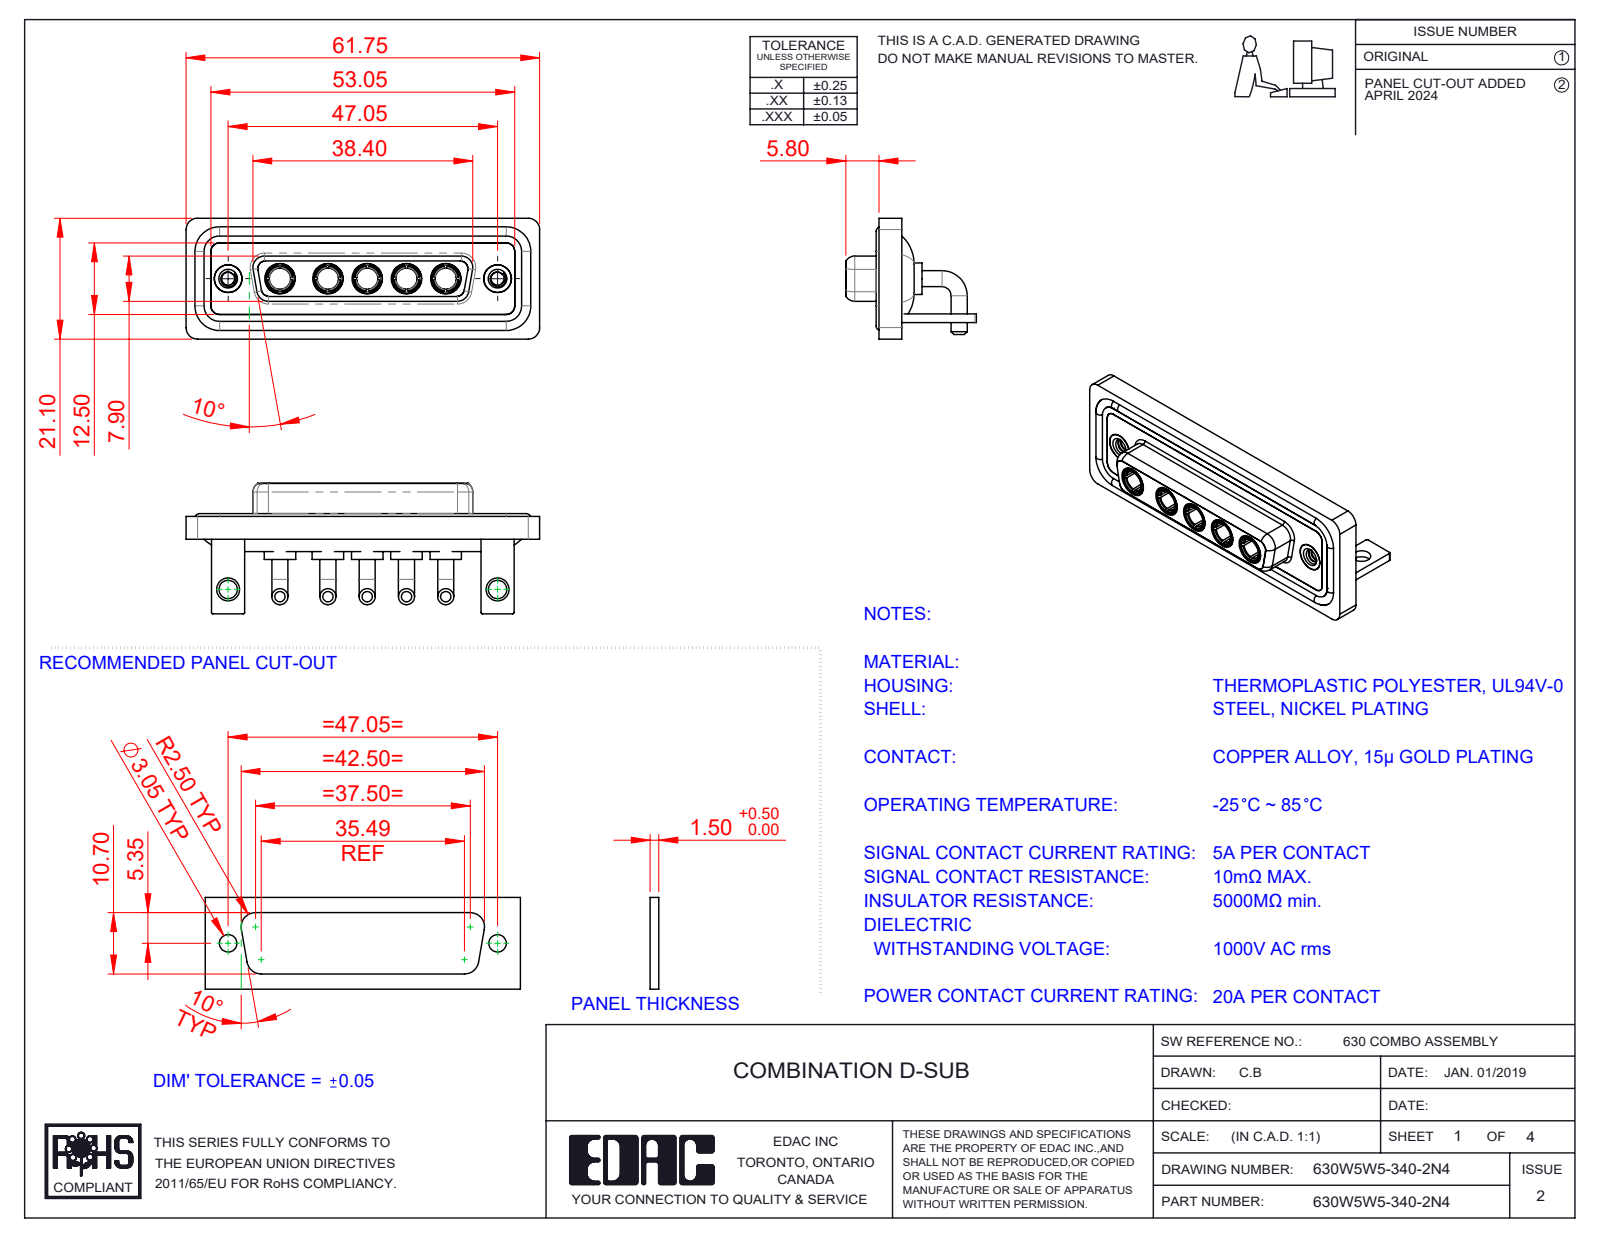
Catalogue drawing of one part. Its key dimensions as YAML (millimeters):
part_name: "630Combo Stabilizer Bracket_50 Contacts; 630Combo Shell Front_25 Contacts; Power Socket_20A RA; 630Combo Housing_5W5 (+4 more)"
step_written_by: "SolidWorks 2023 (CONFIG_CONTROL_DESIGN)"
units: millimeters
bodies: {solids: 19, faces: 824, planar: 270, cylindrical: 337, other: 217}
overall_size: [61.75, 22.8, 21.1]
volume: 8801
surface_area: 14548
round_holes:
  - {diameter: 4.85, count: 7}
  - {diameter: 3.7, count: 5}
  - {diameter: 5.3, count: 5}
  - {diameter: 2.26, count: 2}
  - {diameter: 3.2, count: 2}
  - {diameter: 4, count: 2}
  - {diameter: 4.05, count: 2}
  - {diameter: 5, count: 2}
round_bosses_or_shafts:
  - {diameter: 2.8, count: 10}
  - {diameter: 5.5, count: 5}
  - {diameter: 5.2, count: 5}
  - {diameter: 4.96, count: 5}
  - {diameter: 4.75, count: 5}
  - {diameter: 3.75, count: 5}
  - {diameter: 1.6, count: 4}
  - {diameter: 4.95, count: 2}
partial_cylinders:
  - {radius: 2, count: 19}
  - {radius: 1.5, count: 18}
  - {radius: 0.25, count: 16}
  - {radius: 1.35, count: 8}
  - {radius: 1.6, count: 8}
  - {radius: 0.5, count: 5}
  - {radius: 2.1, count: 5}
  - {radius: 0.6, count: 4}
face_to_face_distances: [0.4, 1.8, 2.9, 3.7, 1.5, 4.1, 1.1, 1.4, 1.6, 2.5]
hole_center_spacings: [6.86, 9.04, 38.01, 47.05, 6.87, 8.38, 13.72, 13.73]
